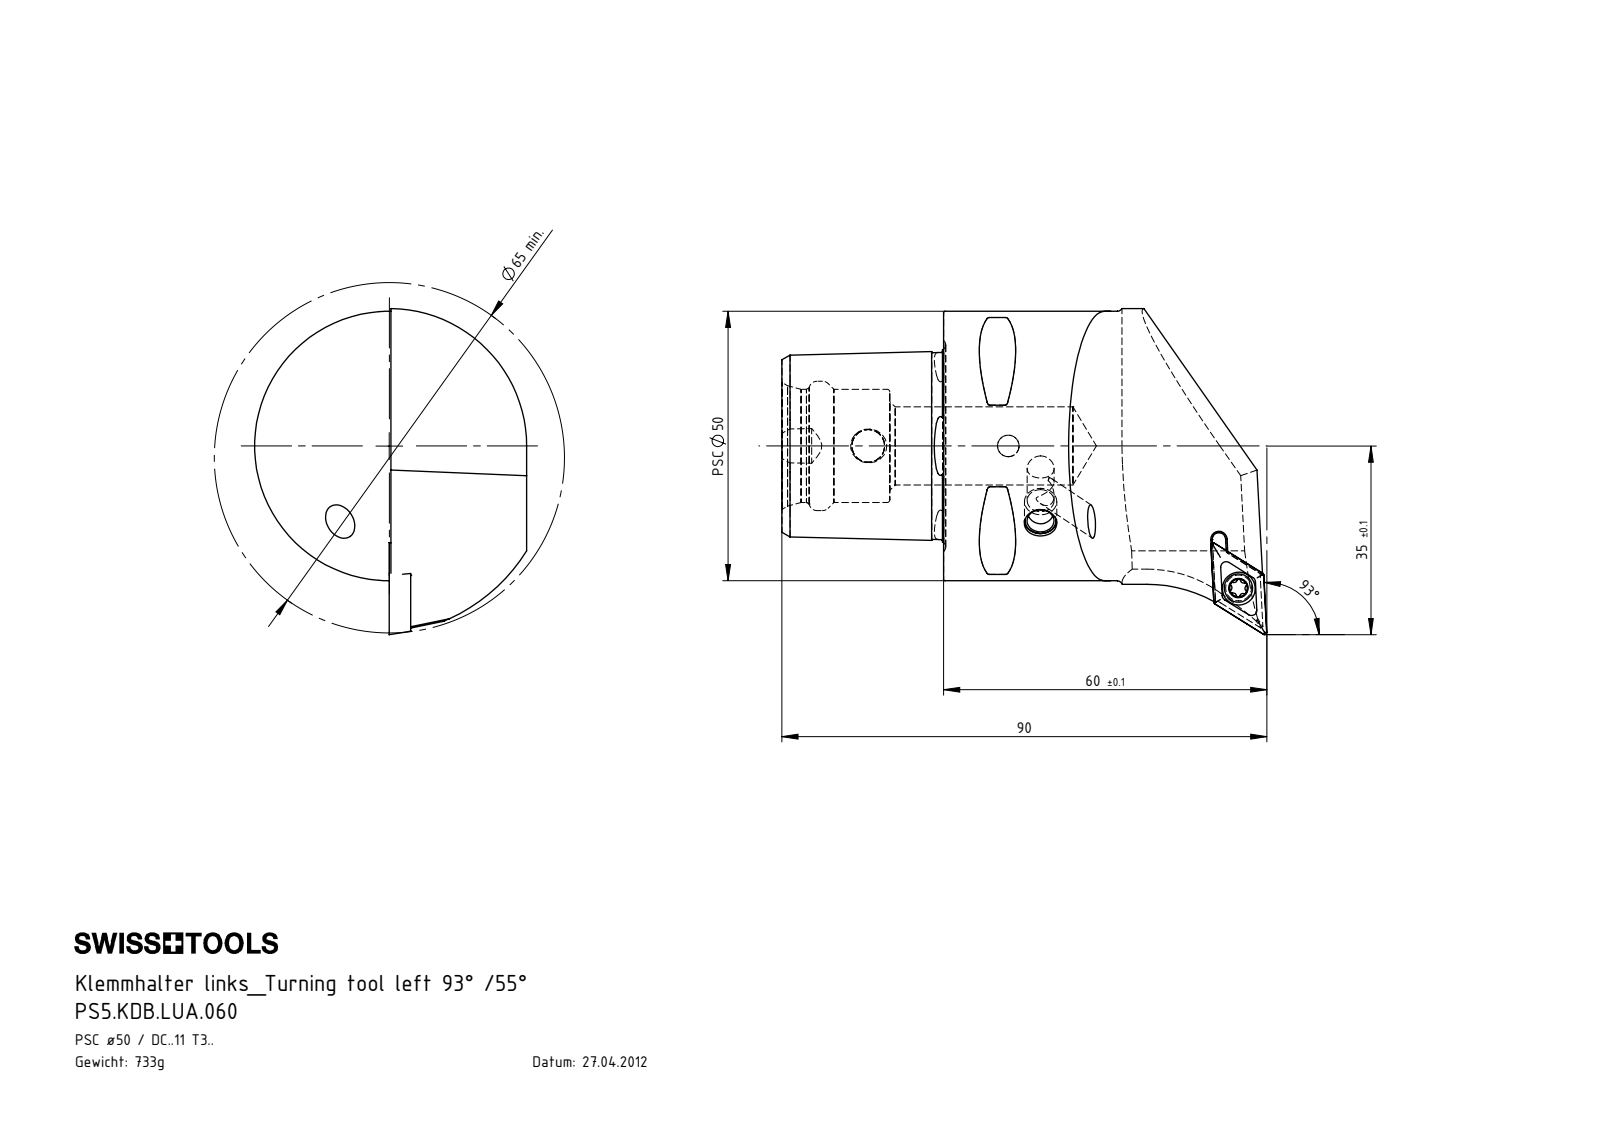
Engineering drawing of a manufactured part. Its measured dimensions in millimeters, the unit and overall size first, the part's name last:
Units: millimetres
Overall size (bounding box): 90 × 60.5 × 50.5
Round holes (diameter × count): ⌀5 ×3, ⌀6.1 ×2, ⌀3.3 ×1, ⌀4 ×1, ⌀4.4 ×1, ⌀6 ×1, ⌀14.5 ×1, ⌀21 ×1, ⌀24 ×1
Round bosses / shafts (diameter × count): ⌀50 ×1, ⌀6 ×1, ⌀5.25 ×1, ⌀4 ×1
Partial cylindrical surfaces — rounded edges, fillets, slot ends (radius × count): R0.5 ×8, R0.34 ×6, R0.59 ×6, R1.25 ×1, R3 ×1, R4 ×1, R25.5 ×1, R26 ×1
Main face-to-face distances: 25.2, 30, 19.18, 21.53, 3.67, 44.4, 20, 10, 29.8, 9.8
Hole centre spacings: 26, 50.21, 50.32, 73.62, 73.71
Volume: 93 127 mm³ · Surface area: 19 482 mm²
Bodies: 5 solids, 269 faces (53 planar, 68 cylindrical, 148 other)
Part name (STEP PRODUCT): DCMT11T304; WCB-ER2.001.009_A; PS5.KDB.LUA.060; KVT_MB_600_060 (+1 more)
STEP written by: SolidWorks 2012 (CONFIG_CONTROL_DESIGN)
